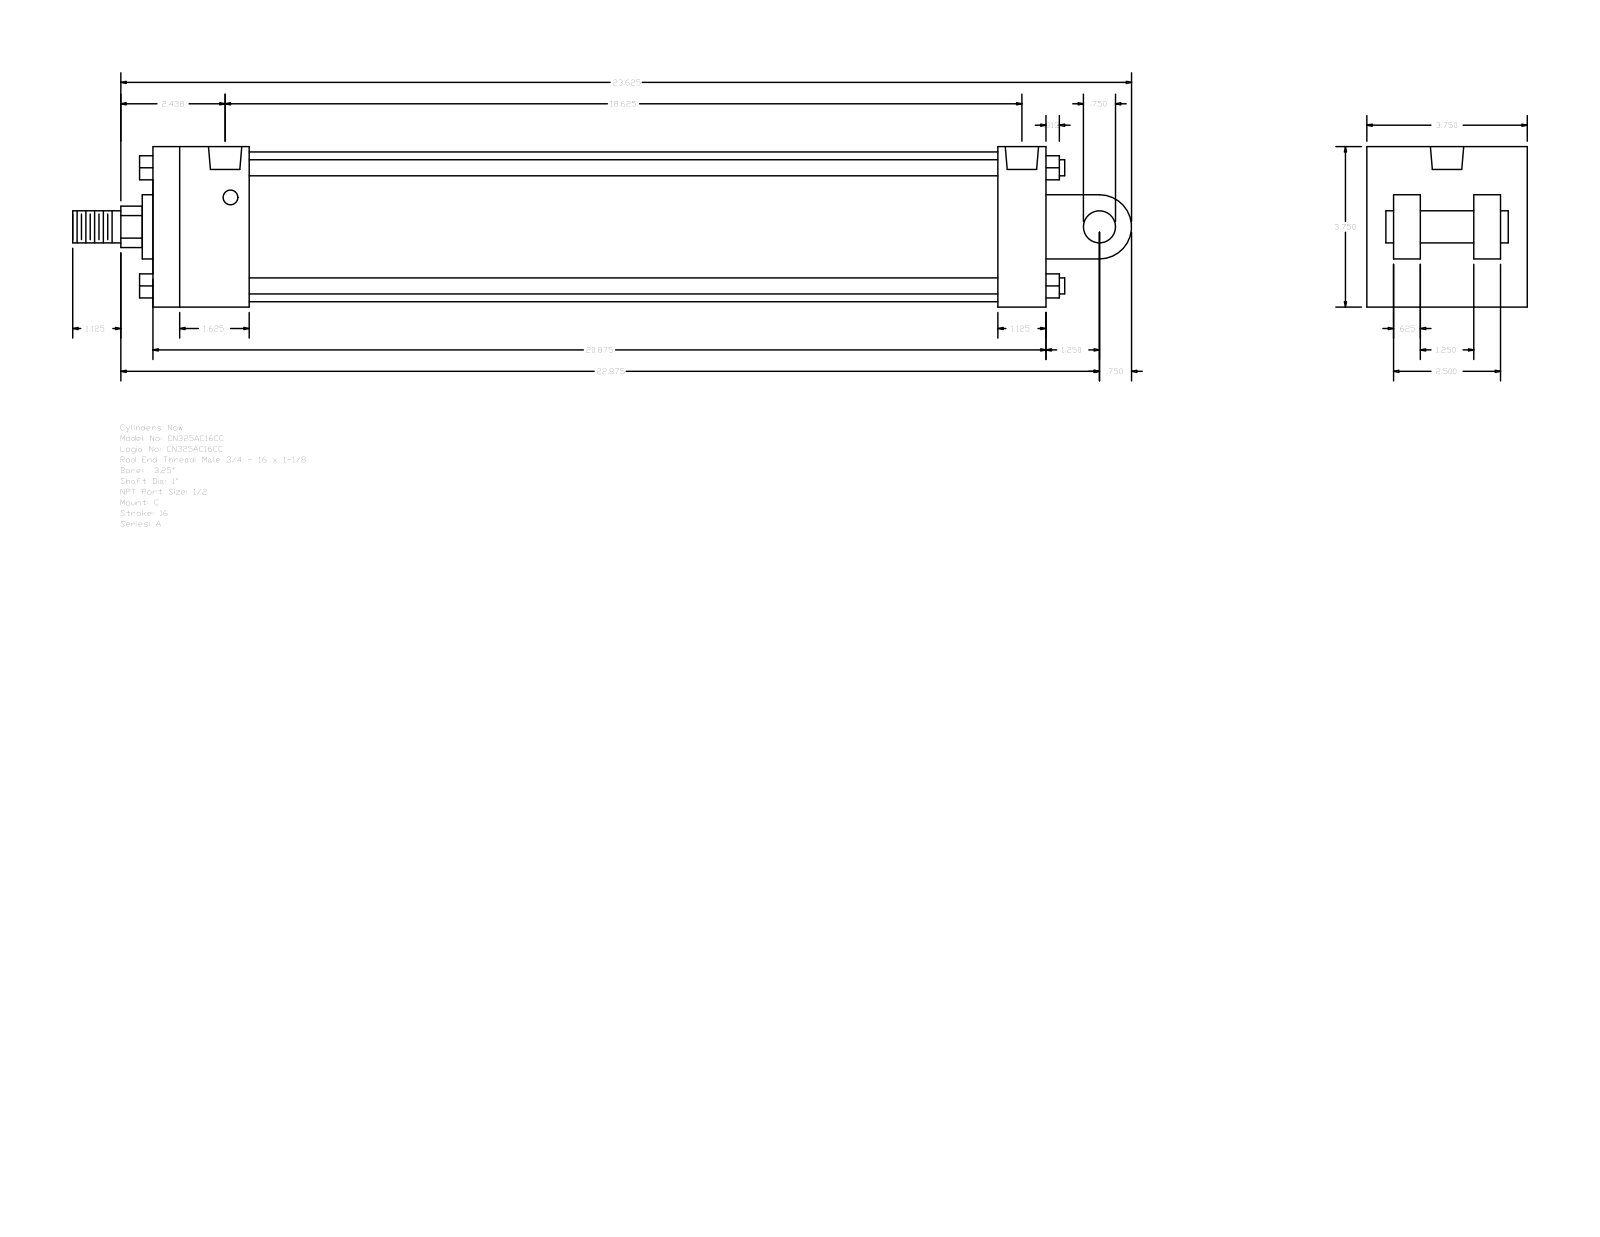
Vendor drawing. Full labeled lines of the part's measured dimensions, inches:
Part name (STEP PRODUCT): A_C__0325_1
STEP written by: GSSL Pune (CONFIG_CONTROL_DESIGN)
Units: inches
Bodies: 0 solids, 135 faces (102 planar, 33 cylindrical, 0 other)
Overall size (bounding box): 24.75 × 3.75 × 3.75
Round holes (diameter × count): ⌀0.344 ×4, ⌀0.778 ×2
Round bosses / shafts (diameter × count): ⌀0.375 ×4, ⌀0.75 ×2, ⌀3.5 ×1, ⌀1.5 ×1, ⌀1 ×1
Partial cylindrical surfaces — rounded edges, fillets, slot ends (radius × count): R0.484 ×1, R0.75 ×1
Main face-to-face distances: 3.75, 20.875, 0.625, 2.5, 1.125, 1.25, 3.125, 1.875, 2.625, 19.75
Hole centre spacings: 0.125, 18.375, 18.5, 18.625
